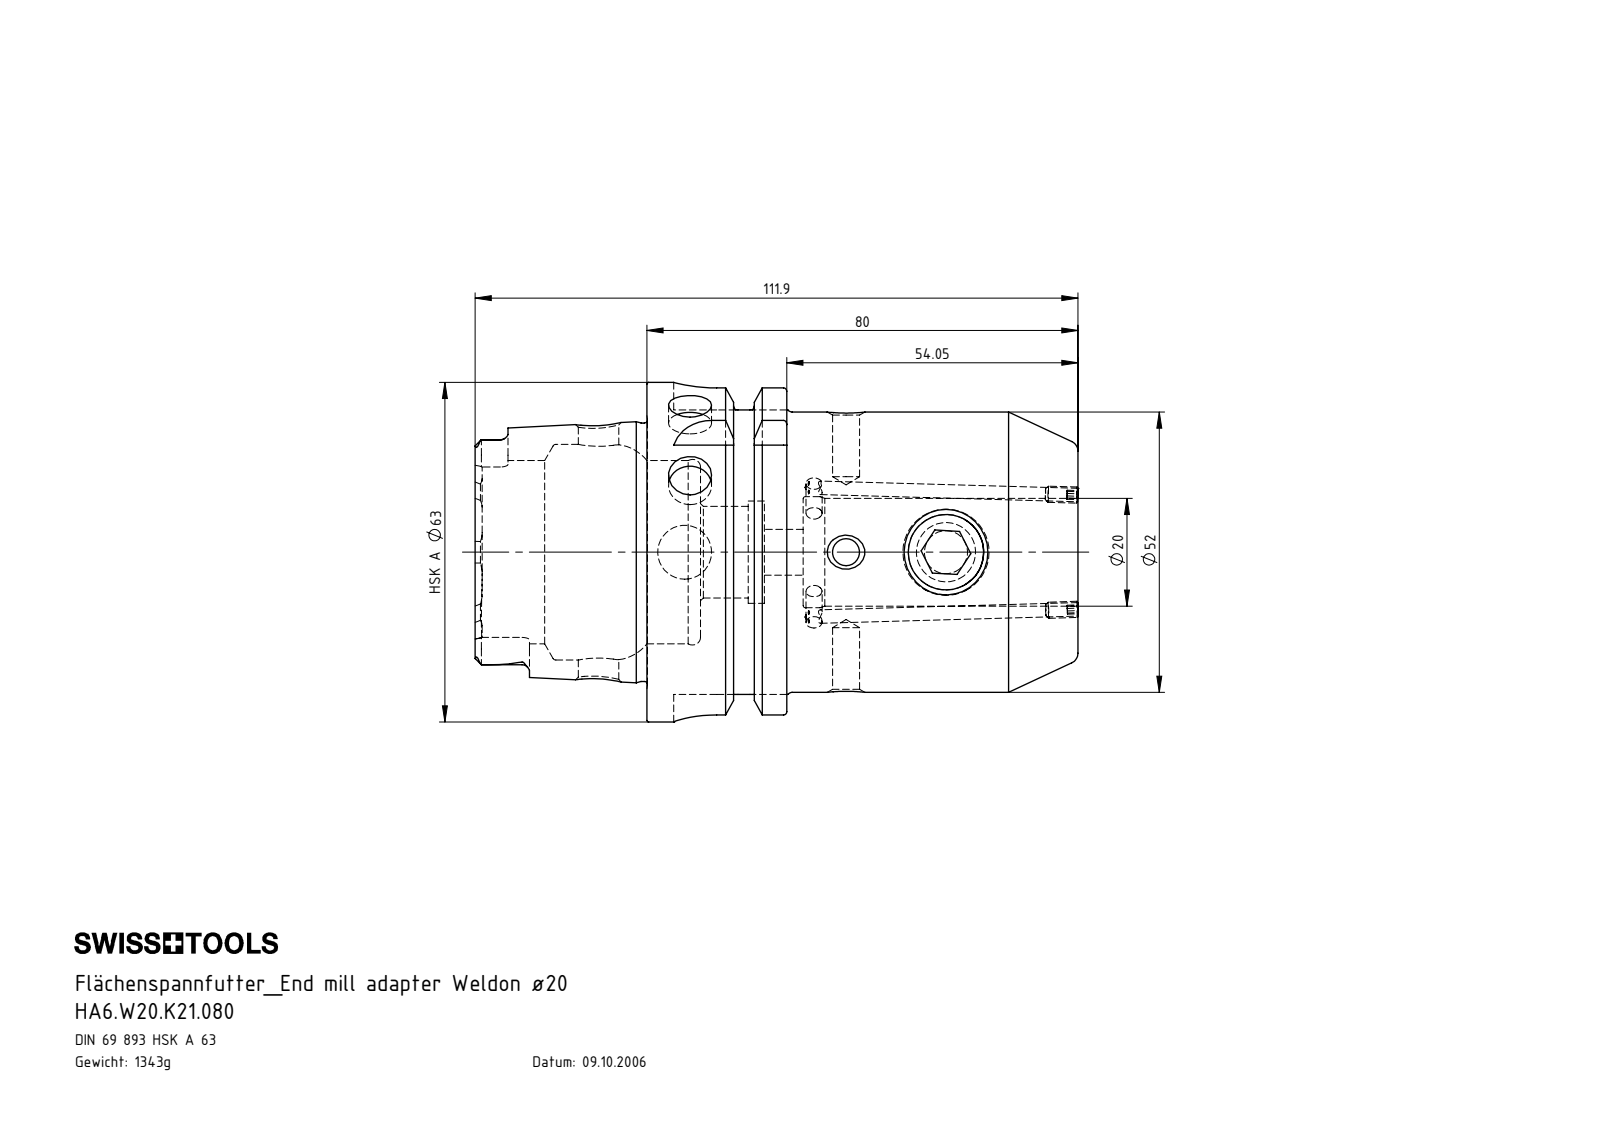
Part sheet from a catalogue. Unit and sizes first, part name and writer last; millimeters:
Units: millimetres
Overall size (bounding box): 111.98 × 63 × 63
Round holes (diameter × count): ⌀2.5 ×2, ⌀5 ×2, ⌀8 ×2, ⌀3 ×1, ⌀7.5 ×1, ⌀8.5 ×1, ⌀10 ×1, ⌀14 ×1, ⌀17 ×1, ⌀19 ×1, ⌀20 ×1, ⌀20.6 ×1
Round bosses / shafts (diameter × count): ⌀3 ×2, ⌀63 ×1, ⌀54.95 ×1, ⌀52 ×1, ⌀47.94 ×1, ⌀16 ×1
Partial cylindrical surfaces — rounded edges, fillets, slot ends (radius × count): R1.4 ×6, R2.88 ×4, R8 ×4
Main face-to-face distances: 80, 25.95, 54.05, 16, 9.95, 70.05, 31.9, 41.85, 57.85, 111.9
Hole centre spacings: 18.55, 29.95, 45.95, 48.5
Volume: 171 040 mm³ · Surface area: 37 261 mm²
Bodies: 4 solids, 287 faces (78 planar, 81 cylindrical, 128 other)
Part name (STEP PRODUCT): W20-ER1.001.016; HA6-W20.K21.080_C_Fertigbearbeitung; ERU-CJ2.001.006; HA6.W20.K21.080
STEP written by: SolidWorks 2012 (CONFIG_CONTROL_DESIGN)
